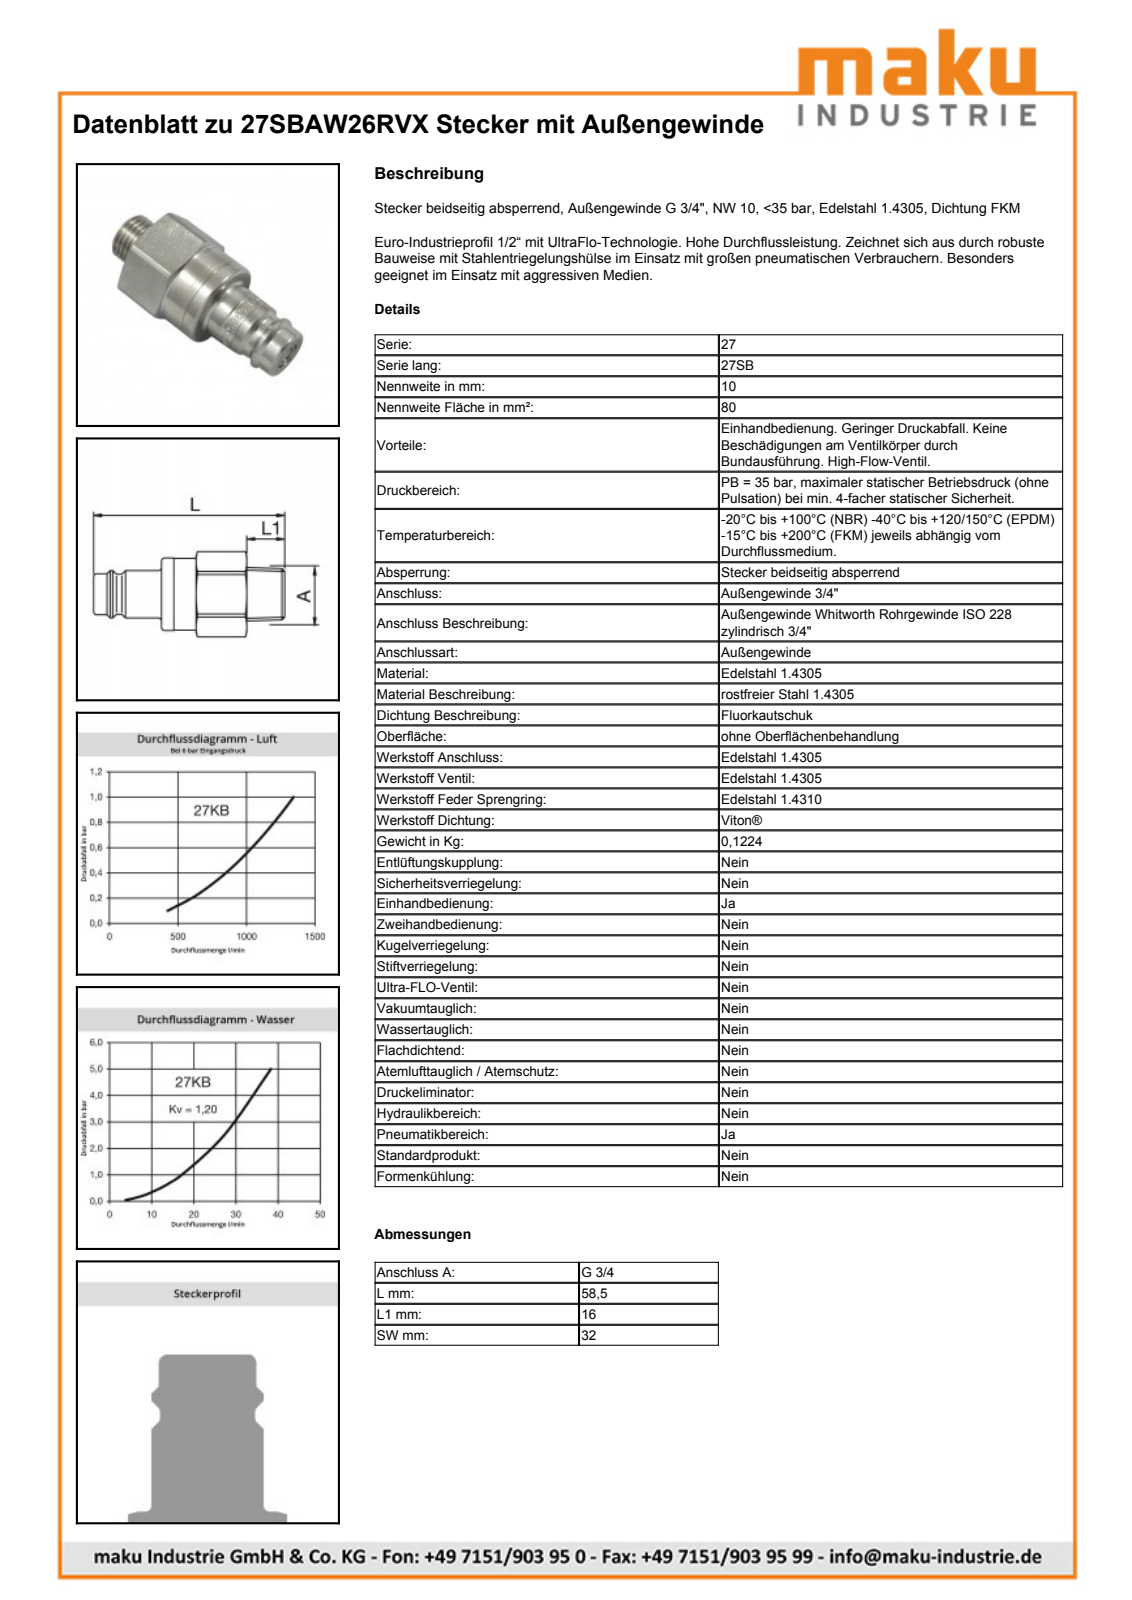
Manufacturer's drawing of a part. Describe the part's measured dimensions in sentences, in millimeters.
The part is named "D110813". Its 3-D file was written by "Autodesk Inventor 2013 (AUTOMOTIVE_DESIGN)". It is 1 solid with 56 faces: 13 planar, 16 cylindrical and 27 other. Overall it measures 58.4 by 35.31 by 35.15 millimeters. Its volume is 25 116 cubic millimeters and its surface area 6 097 square millimeters. Round holes: 1 of diameter 19, 1 of diameter 20.3. Round bosses or shafts: 1 of diameter 26.44, 1 of diameter 23, 1 of diameter 22.75, 1 of diameter 18.5, 1 of diameter 15, 1 of diameter 13, 1 of diameter 12.65. Partial cylindrical surfaces (rounded edges, fillets, slot ends): 1 of radius 18.05. The main face-to-face distances are 25.95, 32, 9.95, 16, 31.98, 10.95, 20.9, 36.9, 21.5, 32.45.
